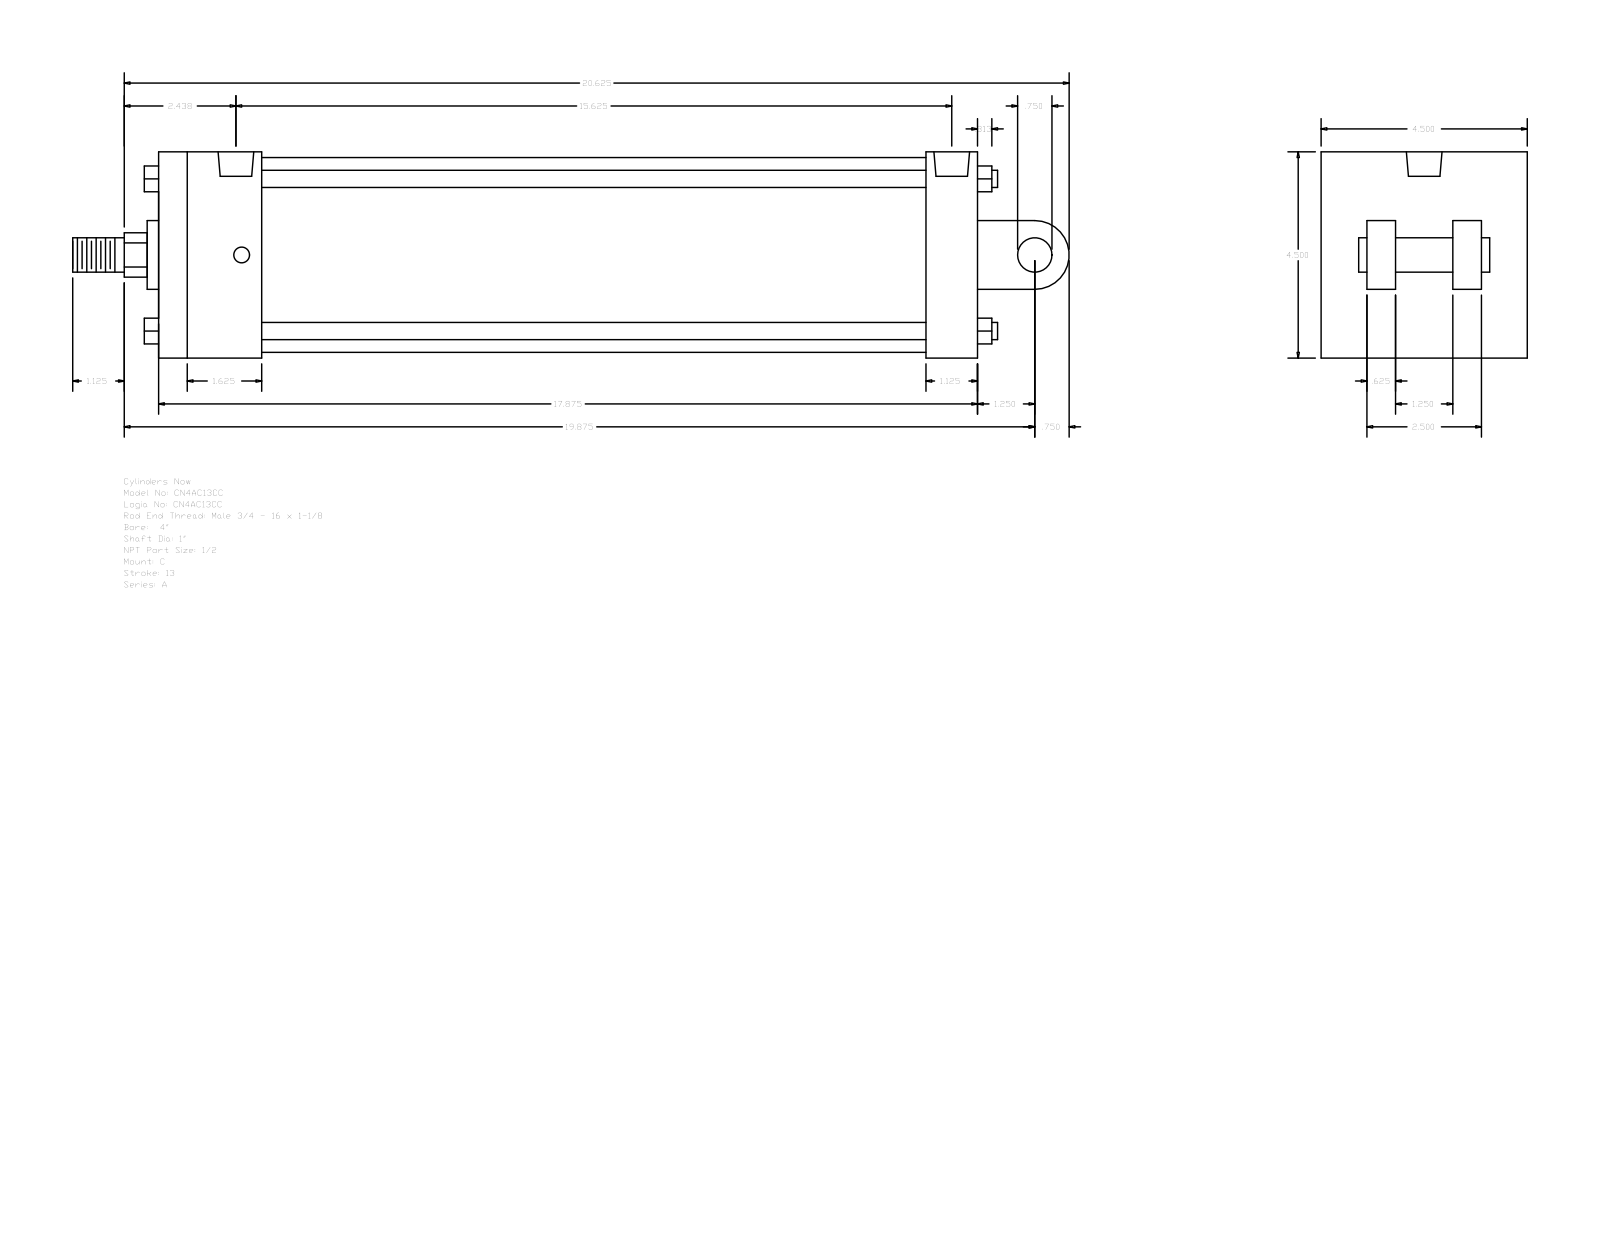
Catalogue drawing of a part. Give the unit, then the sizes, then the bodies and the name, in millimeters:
Units: millimetres
Overall size (bounding box): 552.45 × 114.3 × 114.3
Round holes (diameter × count): ⌀8.73 ×4, ⌀19.77 ×2
Round bosses / shafts (diameter × count): ⌀9.53 ×4, ⌀19.05 ×2, ⌀107.95 ×1, ⌀38.1 ×1, ⌀25.4 ×1
Partial cylindrical surfaces — rounded edges, fillets, slot ends (radius × count): R12.29 ×1, R19.05 ×1
Main face-to-face distances: 114.3, 454.02, 73.03, 28.57, 425.45, 57.15, 368.3, 396.87, 41.27, 38.1
Hole centre spacings: 3.18, 390.52, 393.7, 396.88
Bodies: 0 solids, 135 faces (102 planar, 33 cylindrical, 0 other)
Part name (STEP PRODUCT): A_C__0400_1
STEP written by: GSSL Pune (CONFIG_CONTROL_DESIGN)
